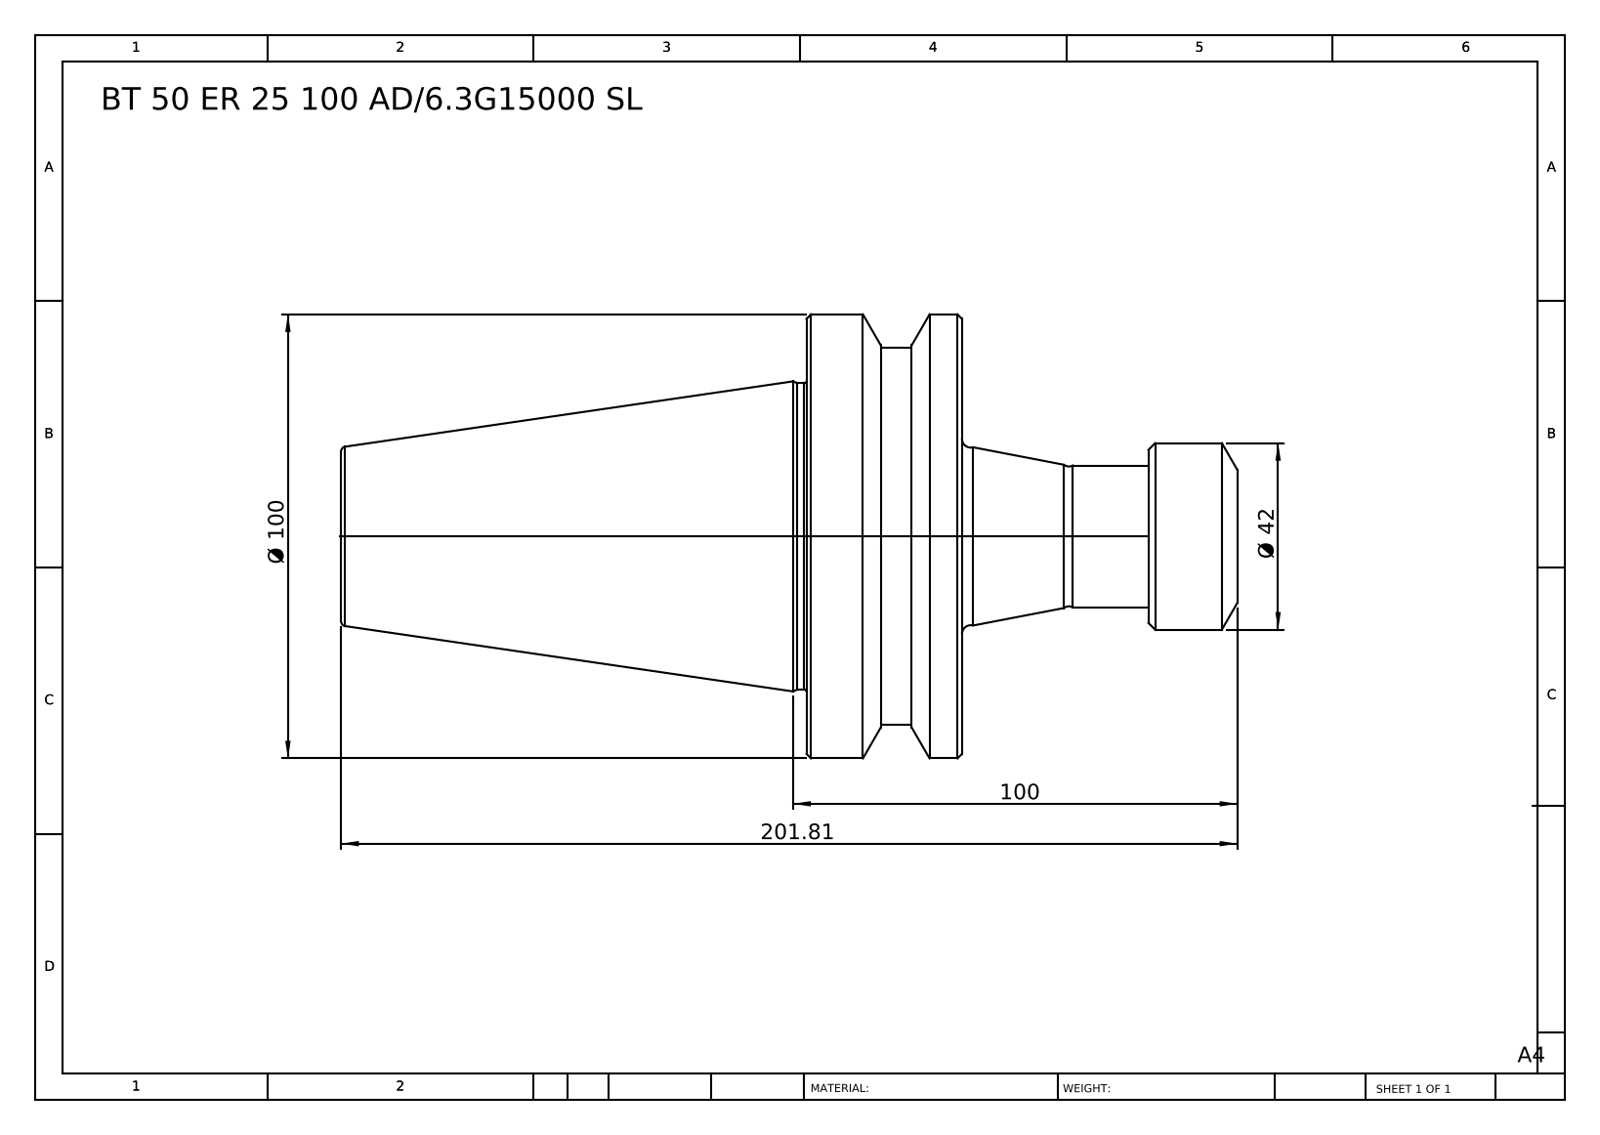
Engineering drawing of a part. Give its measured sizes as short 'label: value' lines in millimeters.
name: BT 50 ER 25 100 AD-6.3G15000 SL
written by: SolidWorks 2014 (CONFIG_CONTROL_DESIGN)
unit: mm
bodies: 1 solid, 51 faces (7 planar, 12 cylindrical, 32 other)
size: 201.81 × 100 × 100
volume: 575 973 mm³; area: 51 748 mm²
bosses: 1× ⌀100, 1× ⌀85, 1× ⌀69, 1× ⌀42, 1× ⌀31.9
face distances: 35, 139.8, 104.8, 62.01, 97.01, 201.81, 20, 42.01, 77.01, 181.81
